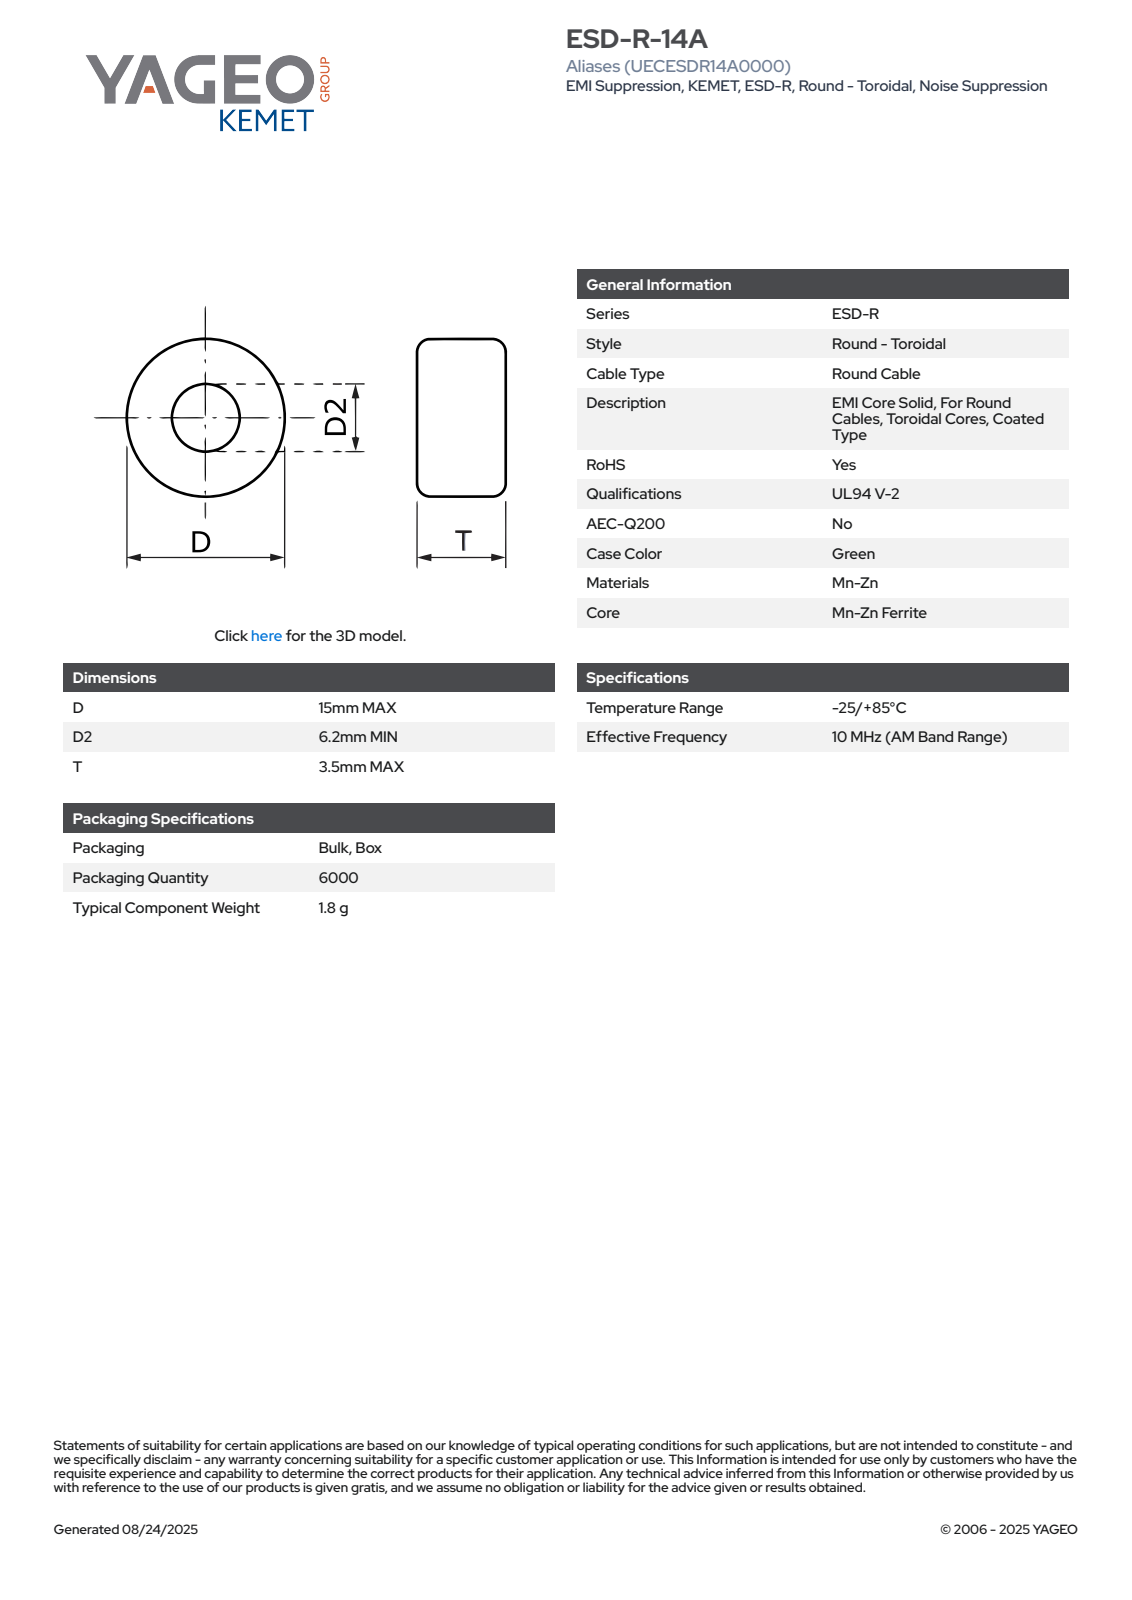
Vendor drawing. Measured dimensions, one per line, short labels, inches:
name: EC_KBC_D15D26.2T3.5
written by: SolidWorks 2021 (AUTOMOTIVE_DESIGN)
unit: in
bodies: 1 solid, 66 faces (24 planar, 7 cylindrical, 35 other)
size: 0.591 × 0.591 × 0.138
volume: 0.031 in³; area: 0.789 in²
holes: 1× ⌀0.244
bosses: 1× ⌀0.591
rounds: 1× R0.296
face distances: 0.138, 0.035, 0.102, 0.067, 0.013, 0.048, 0.09, 0.054, 0.042, 0.077
